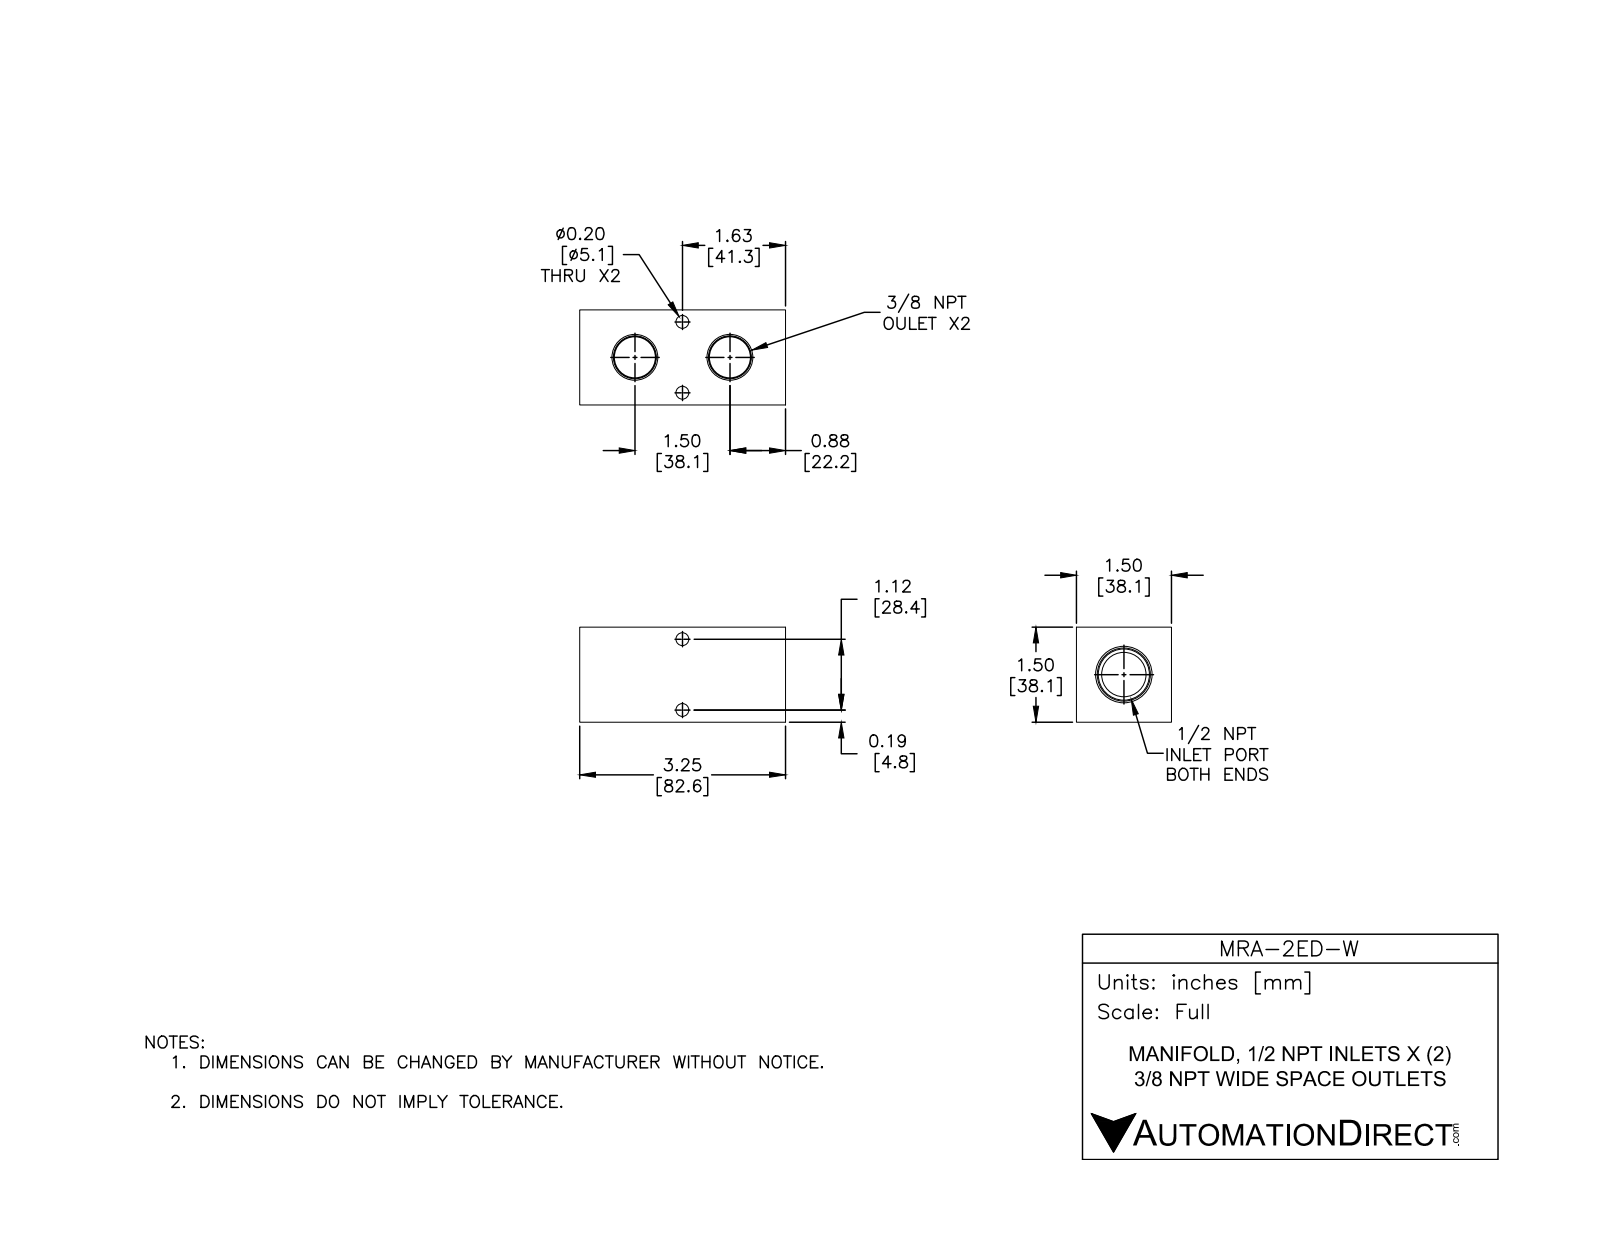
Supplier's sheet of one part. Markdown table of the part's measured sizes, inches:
| quantity | value |
| --- | --- |
| part name | MRA-2ED-W |
| STEP written by | SolidWorks 2015 (CONFIG_CONTROL_DESIGN) |
| units | inches |
| bodies | 1 solid, 58 faces (12 planar, 30 cylindrical, 16 other) |
| overall size | 2.75 × 1.5 × 1.5 |
| volume | 4.5 in³ |
| surface area | 30.11 in² |
| round holes (diameter × count) | 0.2 × 4, 0.562 × 2, 0.703 × 1 |
| main face-to-face distances | 1.5, 2.75, 0.53, 2.22, 1.09, 0.41, 1.69 |
| hole center spacings | 0.751, 1.12, 1 |
